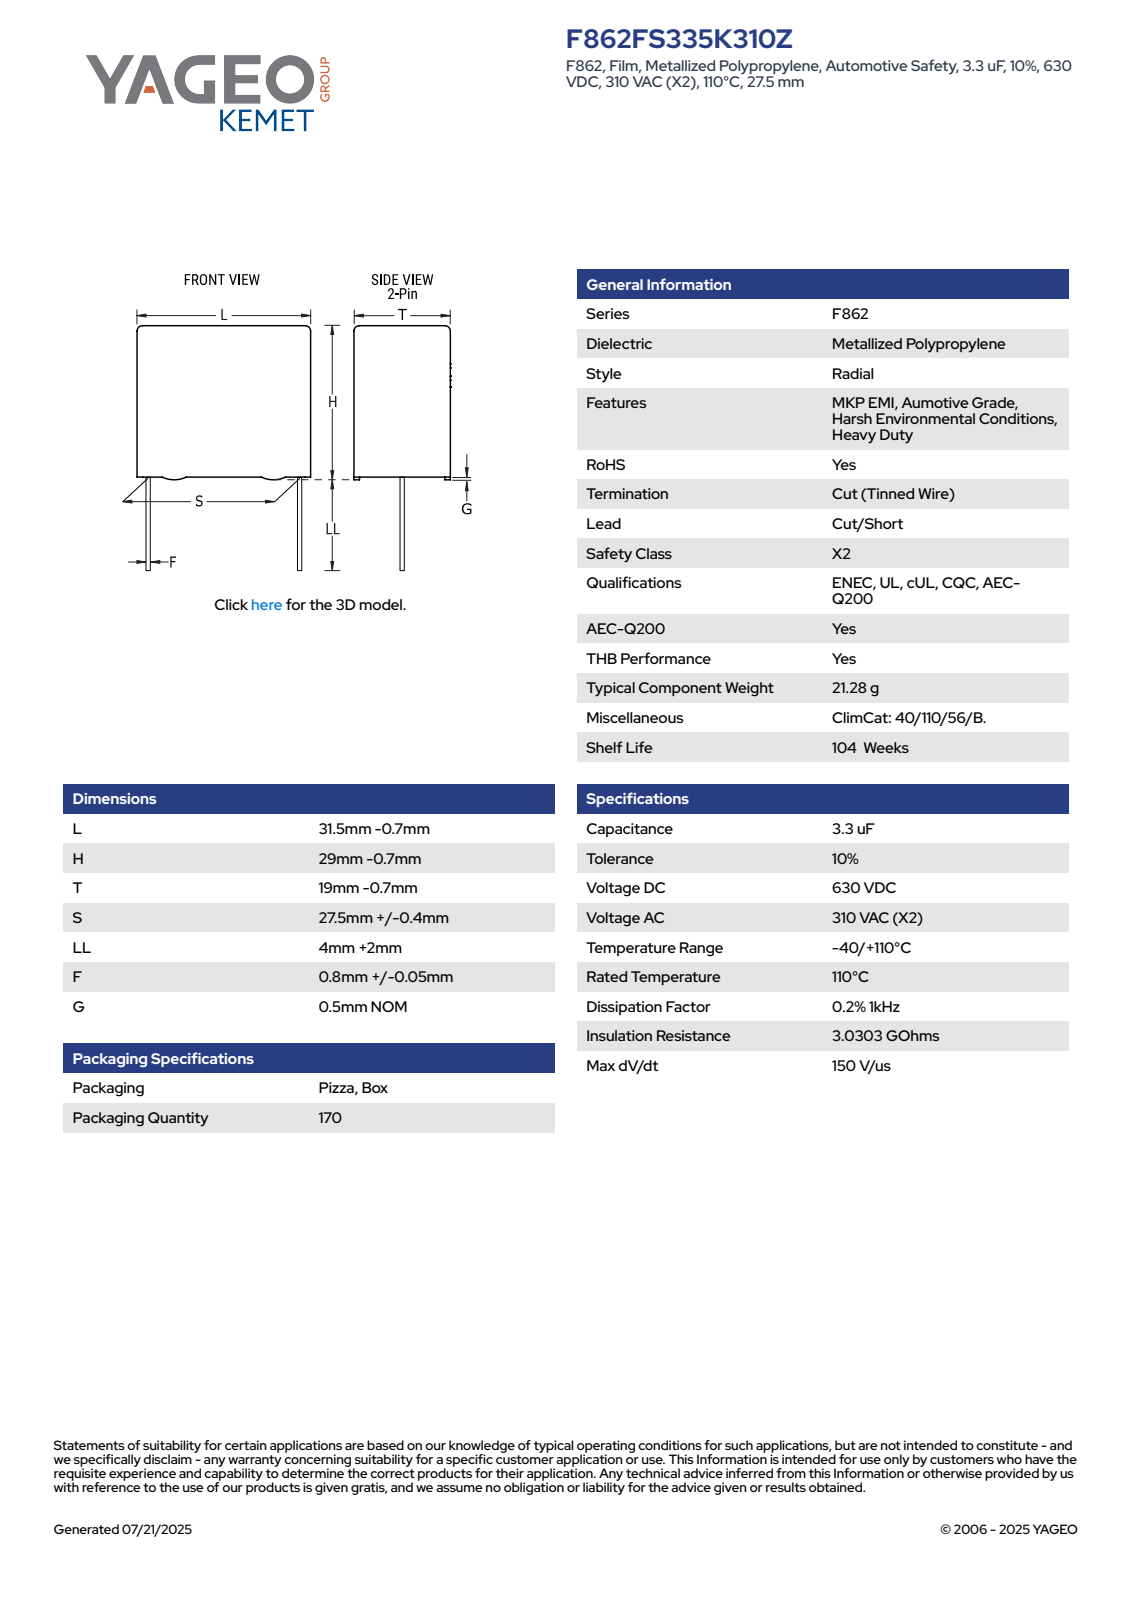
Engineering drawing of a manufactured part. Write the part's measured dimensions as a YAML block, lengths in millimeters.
part_name: "CFR_RBG_31.5X29X19_L30.8H28.3T18.3S27.5LL6F0.85G0.5"
step_written_by: "SolidWorks 2014 (AUTOMOTIVE_DESIGN)"
units: millimeters
bodies: {solids: 4, faces: 89, planar: 81, cylindrical: 8, other: 0}
overall_size: [34.3, 30.8, 18.3]
volume: 15682
surface_area: 3996
round_bosses_or_shafts:
  - {diameter: 0.85, count: 2}
partial_cylinders:
  - {radius: 0.5, count: 4}
face_to_face_distances: [18.3, 27.8, 30.8, 18.31, 0.5, 28.3, 1.04, 17.26, 1.05, 16.22]
